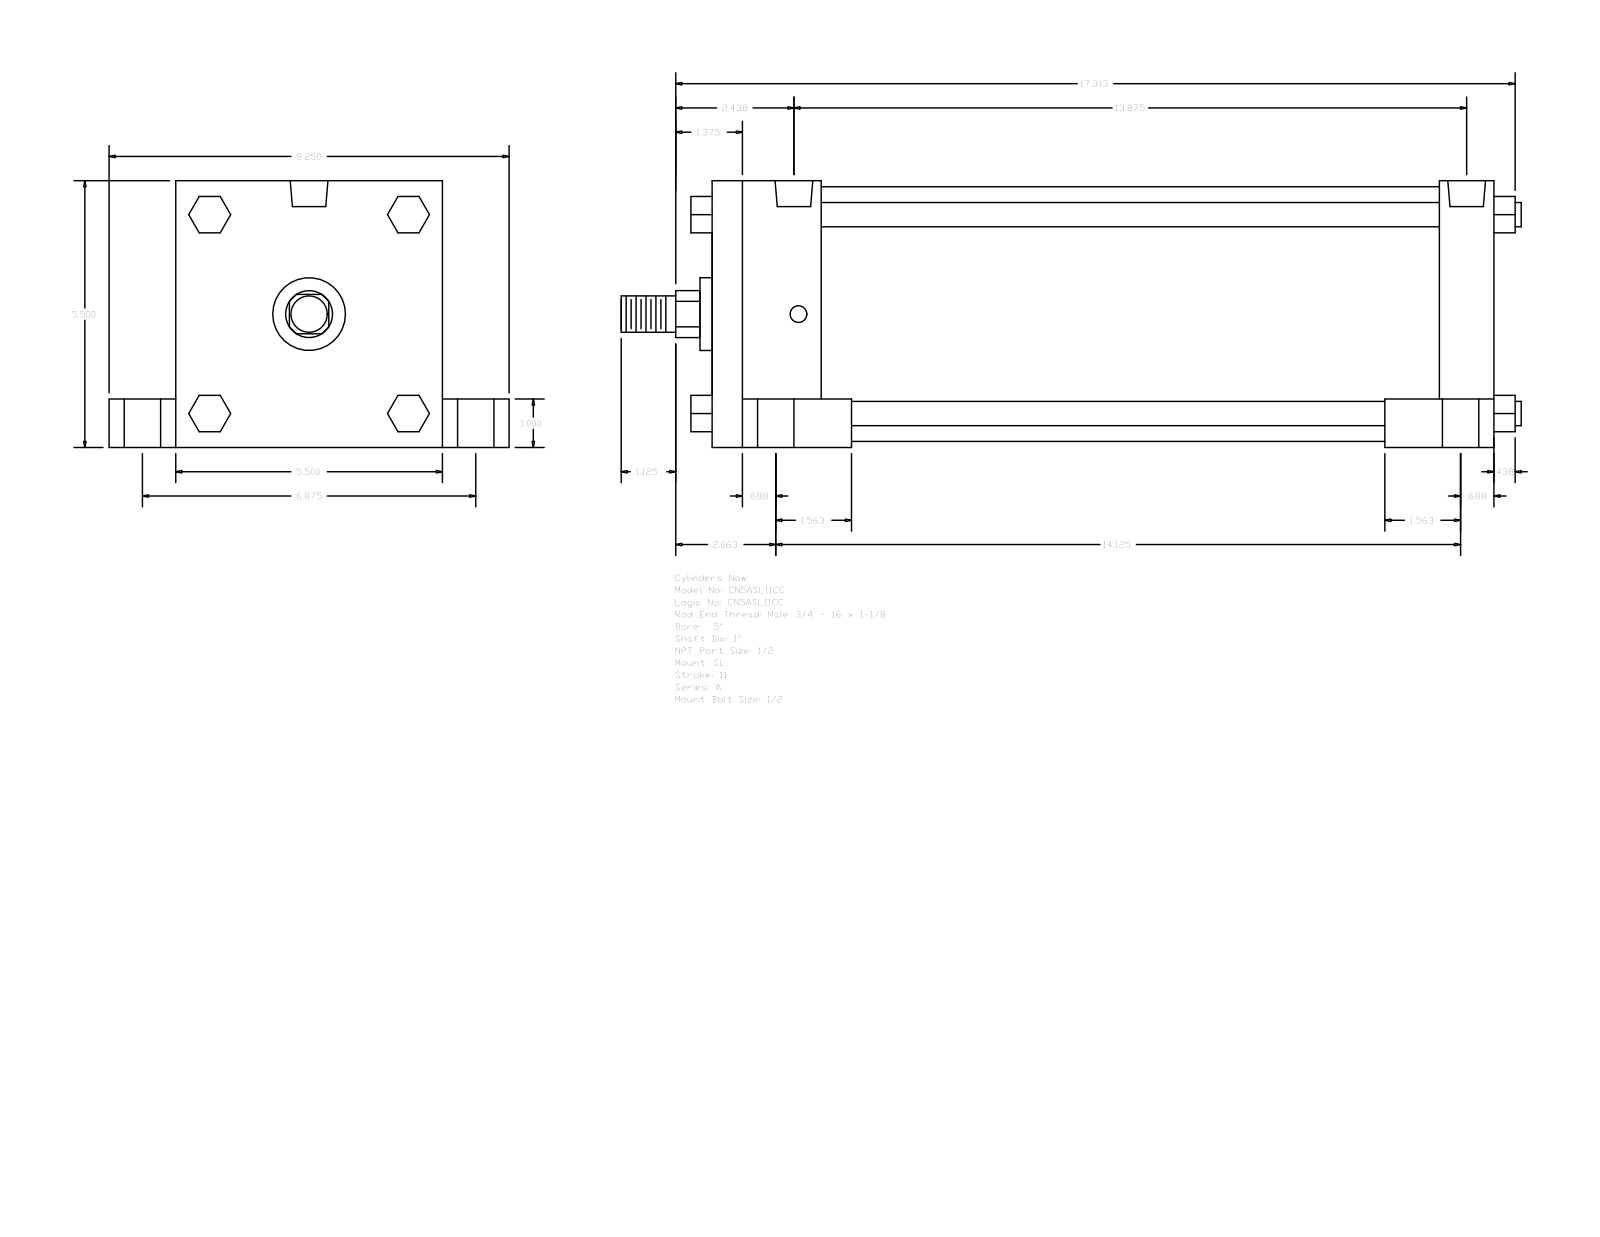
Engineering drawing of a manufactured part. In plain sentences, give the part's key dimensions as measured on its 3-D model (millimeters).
The part is named "A_SL__0500_1". Its 3-D file was written by "GSSL Pune (CONFIG_CONTROL_DESIGN)". It is 0 solids with 150 faces: 114 planar, 36 cylindrical and 0 other. Overall it measures 471.49 by 209.55 by 139.7 millimeters. Round holes: 4 of diameter 8.73, 4 of diameter 19.05, 4 of diameter 25.4, 2 of diameter 19.77. Round bosses or shafts: 4 of diameter 12.7, 1 of diameter 133.35, 1 of diameter 38.1, 1 of diameter 25.4, 1 of diameter 19.05. Partial cylindrical surfaces (rounded edges, fillets, slot ends): 1 of radius 12.29. The main face-to-face distances are 139.7, 409.57, 28.57, 25.4, 114.3, 34.93, 174.63, 57.15, 381, 323.85. The hole center spacings are 2.39, 87.31, 87.37, 87.83, 88.12, 174.62, 347.65, 350.04.
